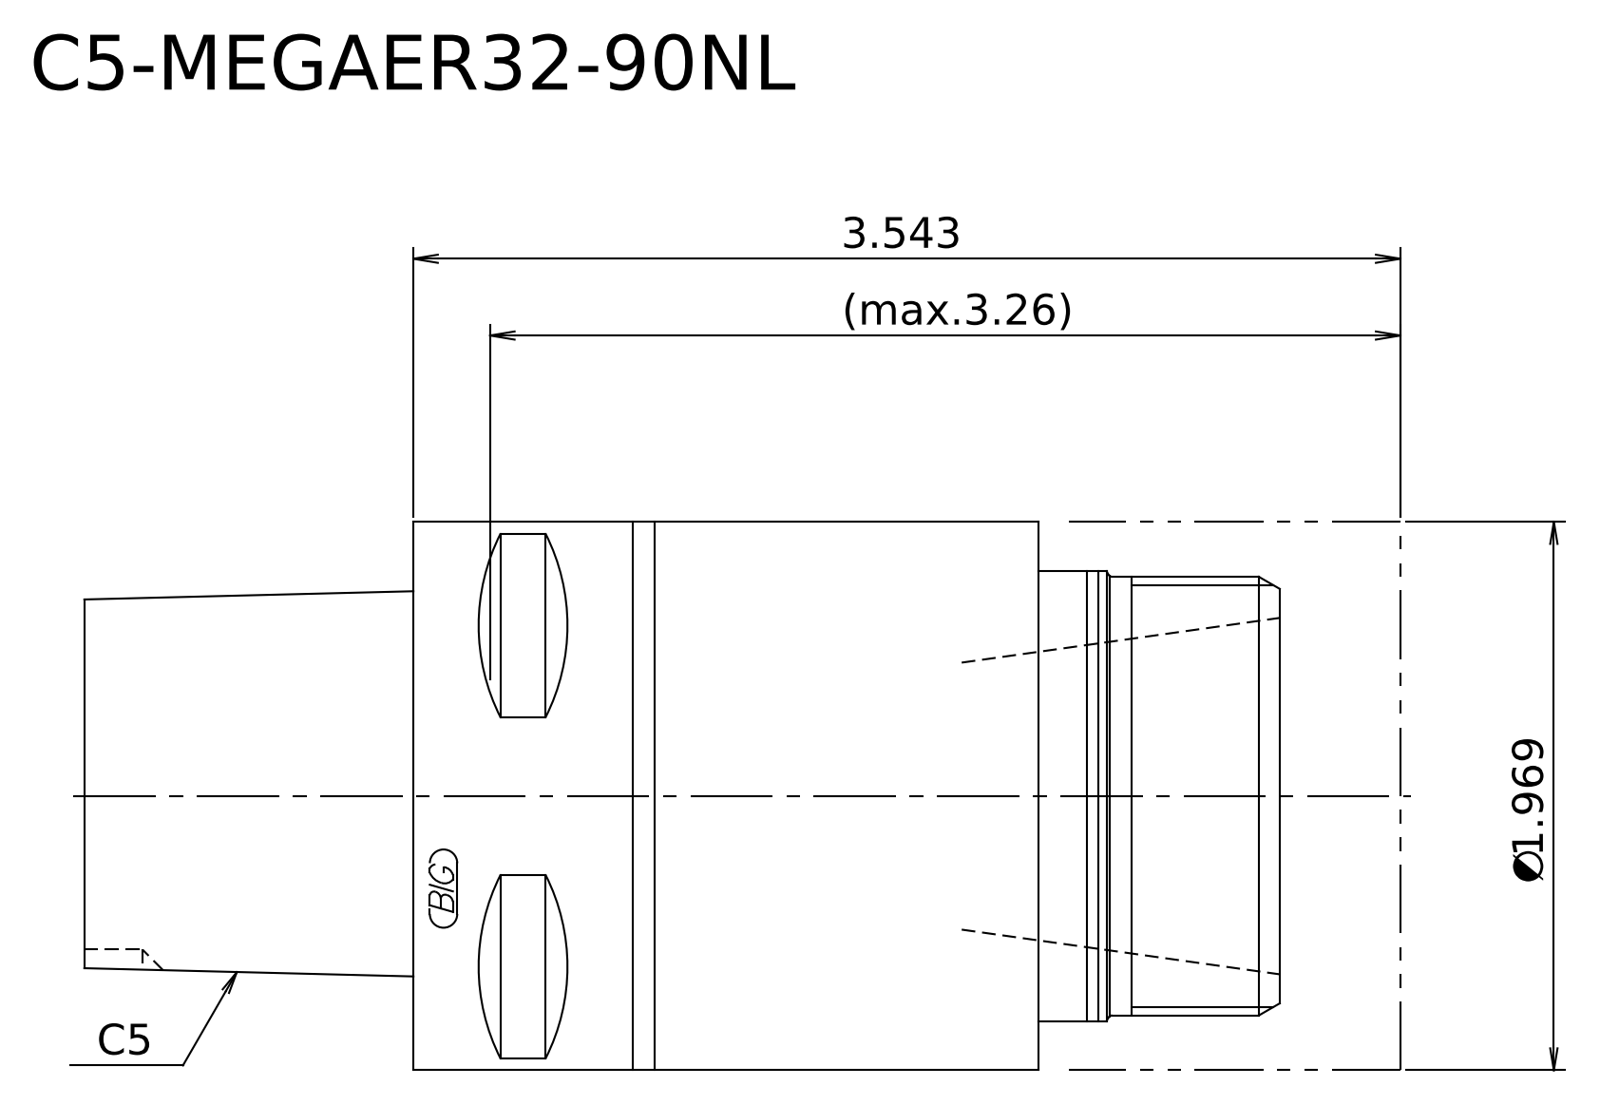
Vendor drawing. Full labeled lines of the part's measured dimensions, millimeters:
STEP written by: Kubotek KeyCreator 2011 V10.0.2 (22737) (automotive_design)
Units: millimetres
Bodies: 2 solids, 13 faces (6 planar, 4 cylindrical, 3 other)
Overall size (bounding box): 120 × 50 × 50
Volume: 226 327 mm³ · Surface area: 27 365 mm²
Round bosses / shafts (diameter × count): ⌀50 ×1, ⌀41 ×1, ⌀40 ×1
Main face-to-face distances: 30.2, 11, 19.2, 90, 79, 59.8, 120, 109, 89.8, 30
